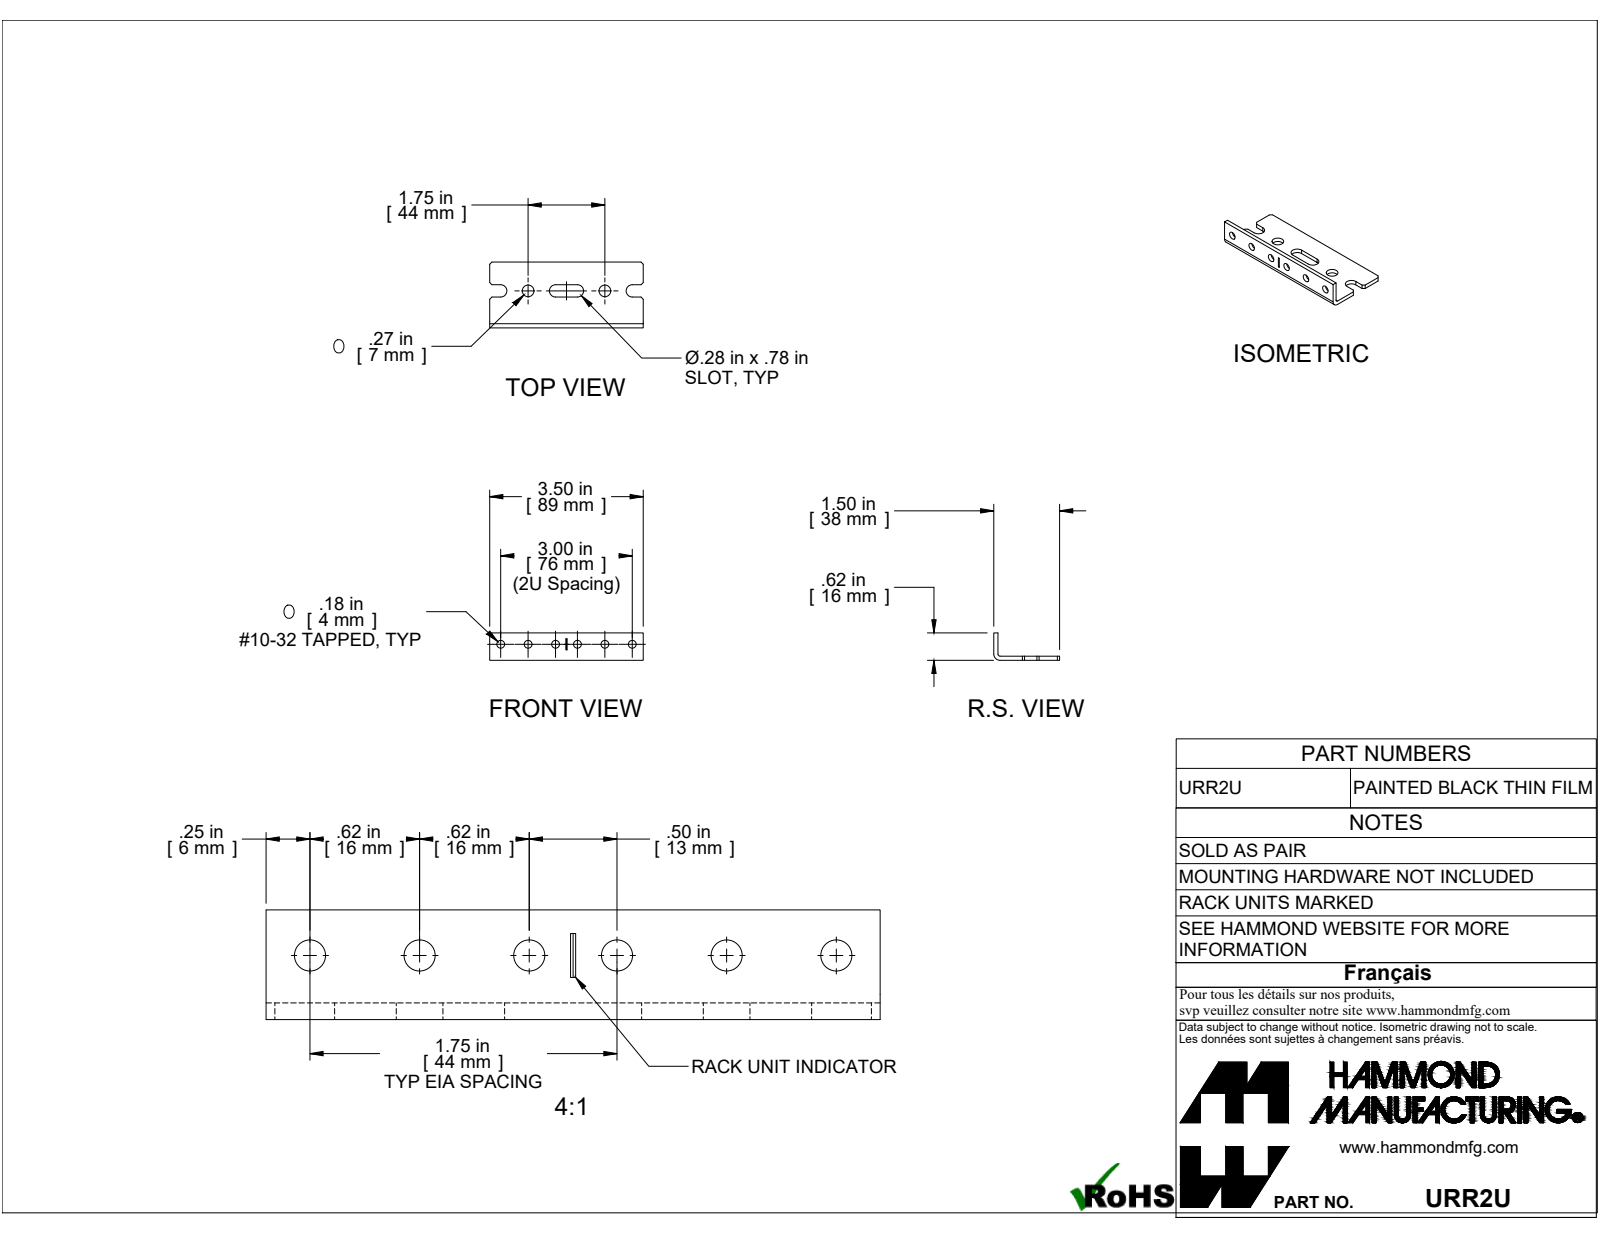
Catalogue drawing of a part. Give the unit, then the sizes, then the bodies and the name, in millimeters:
Units: millimetres
Overall size (bounding box): 88.9 × 38.1 × 15.88
Round holes (diameter × count): ⌀4.5 ×6, ⌀6.76 ×2
Partial cylindrical surfaces — rounded edges, fillets, slot ends (radius × count): R3.57 ×4, R1.22 ×1, R3.63 ×1
Main face-to-face distances: 2.41, 15.88, 13.47, 38.1, 35.69, 88.9, 17.84, 24.98, 15.43, 22.57
Hole centre spacings: 15.87, 15.88, 28.58, 31.75, 44.45, 44.46, 60.33, 12.7
Volume: 9 791 mm³ · Surface area: 9 287 mm²
Bodies: 1 solid, 40 faces (26 planar, 14 cylindrical, 0 other)
Part name (STEP PRODUCT): COM57213-2
STEP written by: ST-DEVELOPER v16.7 (AP203_CONFIGURATION_CONTROLLED_3D_DESIGN_OF_MECHANICAL_PARTS_AND_ASSEMBLIES_MIM_LF)
